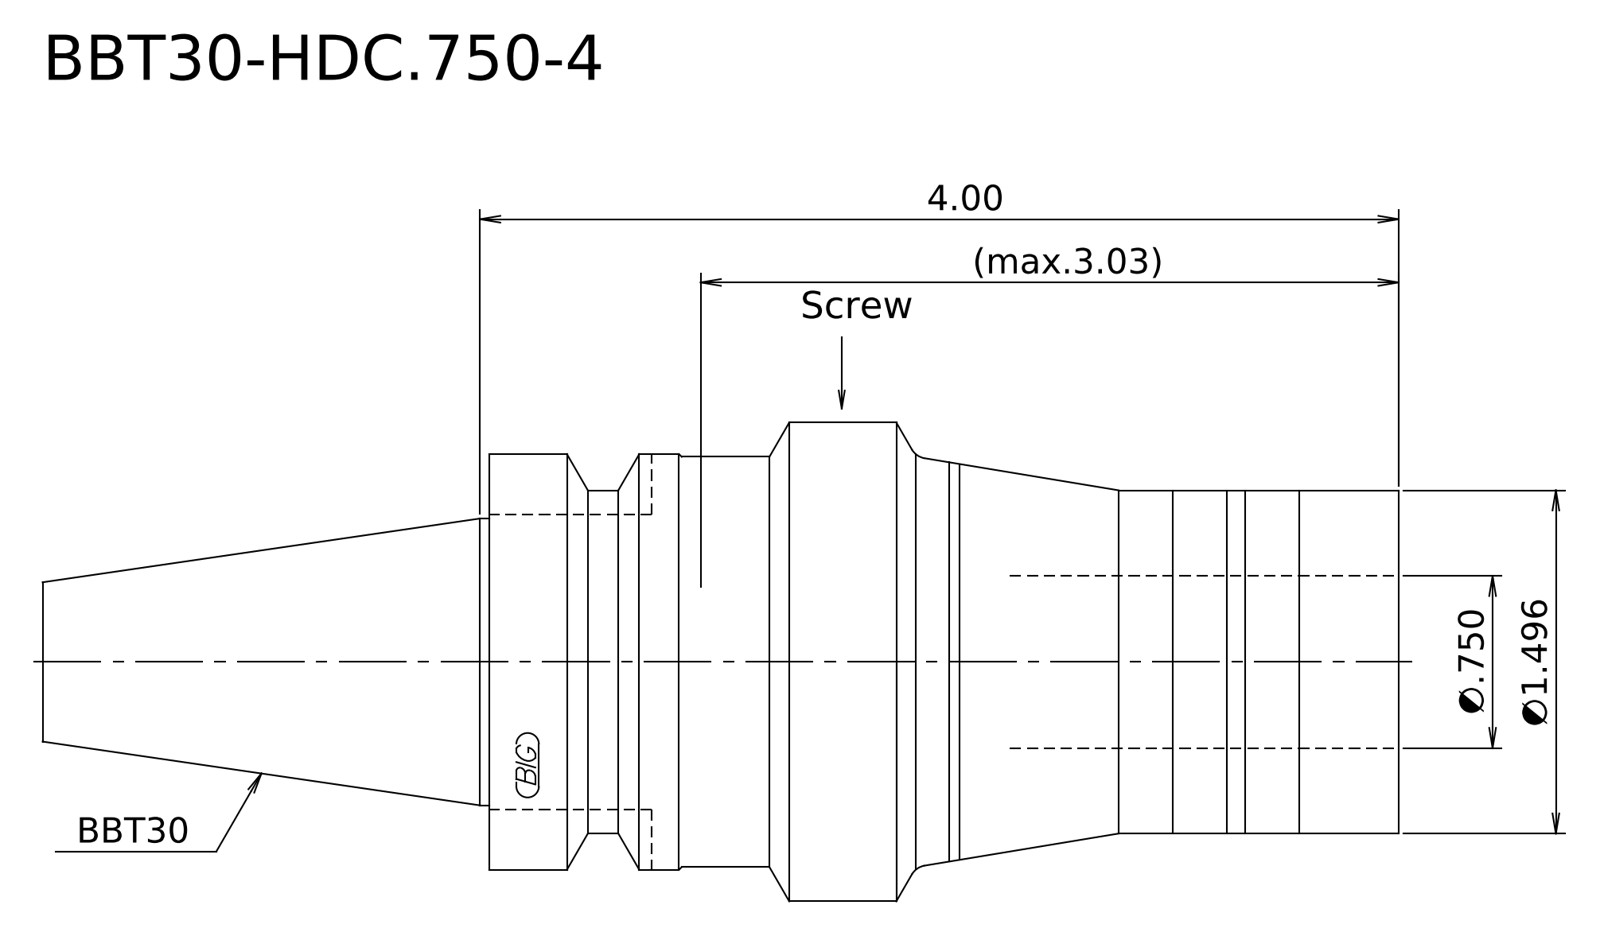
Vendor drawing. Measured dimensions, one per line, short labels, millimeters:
written by: Kubotek KeyCreator 2011 V10.0.2 (22737) (automotive_design)
unit: mm
bodies: 1 solid, 17 faces (3 planar, 7 cylindrical, 7 other)
size: 150 × 53 × 53
volume: 173 166 mm³; area: 21 051 mm²
bosses: 1× ⌀53, 1× ⌀46, 1× ⌀45.4, 1× ⌀38, 1× ⌀31.75
face distances: 100.6, 150, 49.4
